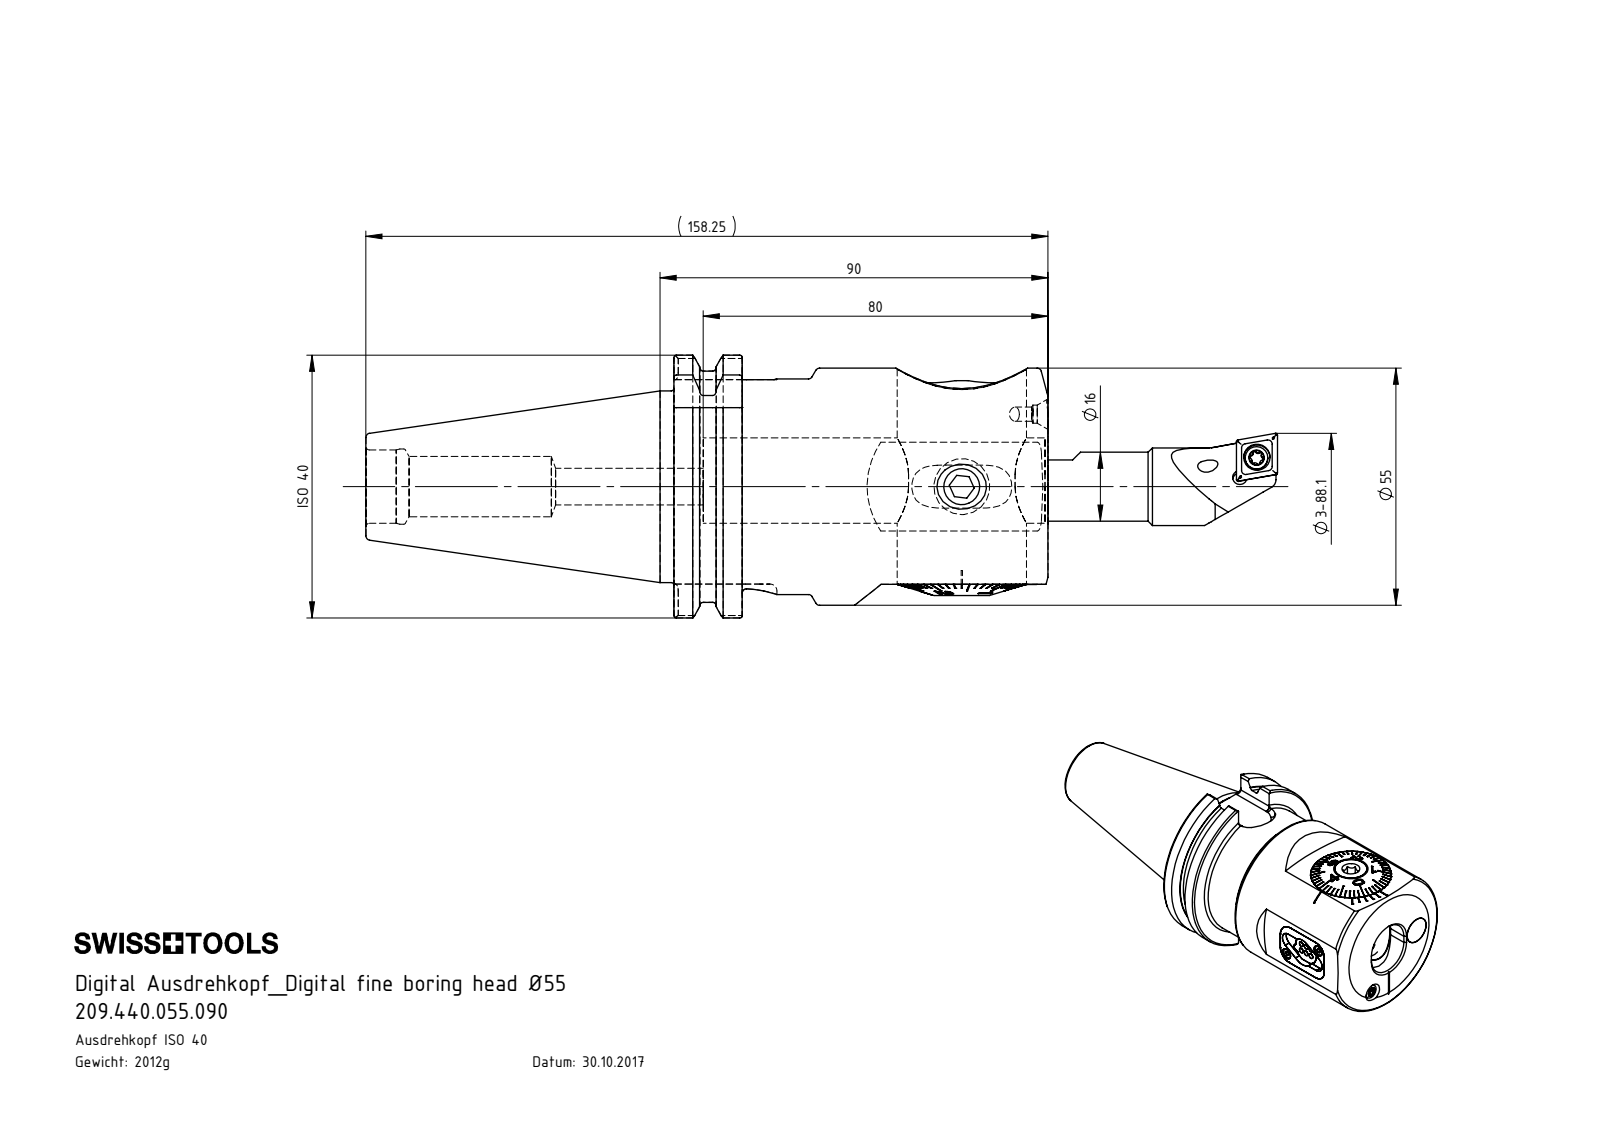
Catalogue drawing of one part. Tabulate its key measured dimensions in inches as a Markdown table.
| quantity | value |
| --- | --- |
| part name | Klebstoff D10; A55-BG2.015.007_A; Fxx-BG7.DA2.0xx_F55; A55-BG2.014.007_A (+8 more) |
| STEP written by | SolidWorks 2017 (CONFIG_CONTROL_DESIGN) |
| units | inches |
| bodies | 29 solids, 1284 faces (544 planar, 339 cylindrical, 401 other) |
| overall size | 8.327 × 2.5 × 2.399 |
| volume | 15.72 in³ |
| surface area | 104.9 in² |
| round holes (diameter × count) | 0.126 × 4, 0.335 × 4, 0.063 × 3, 0.13 × 3, 0.165 × 3, 0.087 × 2, 0.118 × 2, 0.551 × 2, 0.173 × 1, 0.24 × 1, 0.315 × 1, 0.394 × 1 |
| round bosses / shafts (diameter × count) | 0.075 × 6, 0.394 × 3, 0.709 × 2, 0.207 × 2, 0.157 × 2, 0.15 × 2, 0.079 × 2, 2.165 × 1 |
| partial cylindrical surfaces (radius × count) | 0.013 × 12, 0.023 × 12, 0.043 × 9, 0.047 × 8, 0.063 × 8, 0.177 × 5, 0.126 × 3, 0.173 × 3 |
| main face-to-face distances | 3.417, 0.146, 0.624, 2.793, 0.268, 0.079, 1.136, 0.157, 0.018, 0.209 |
| hole center spacings | 0.161, 0.17, 0.285, 0.333, 0.375, 0.472, 0.499, 0.571 |
